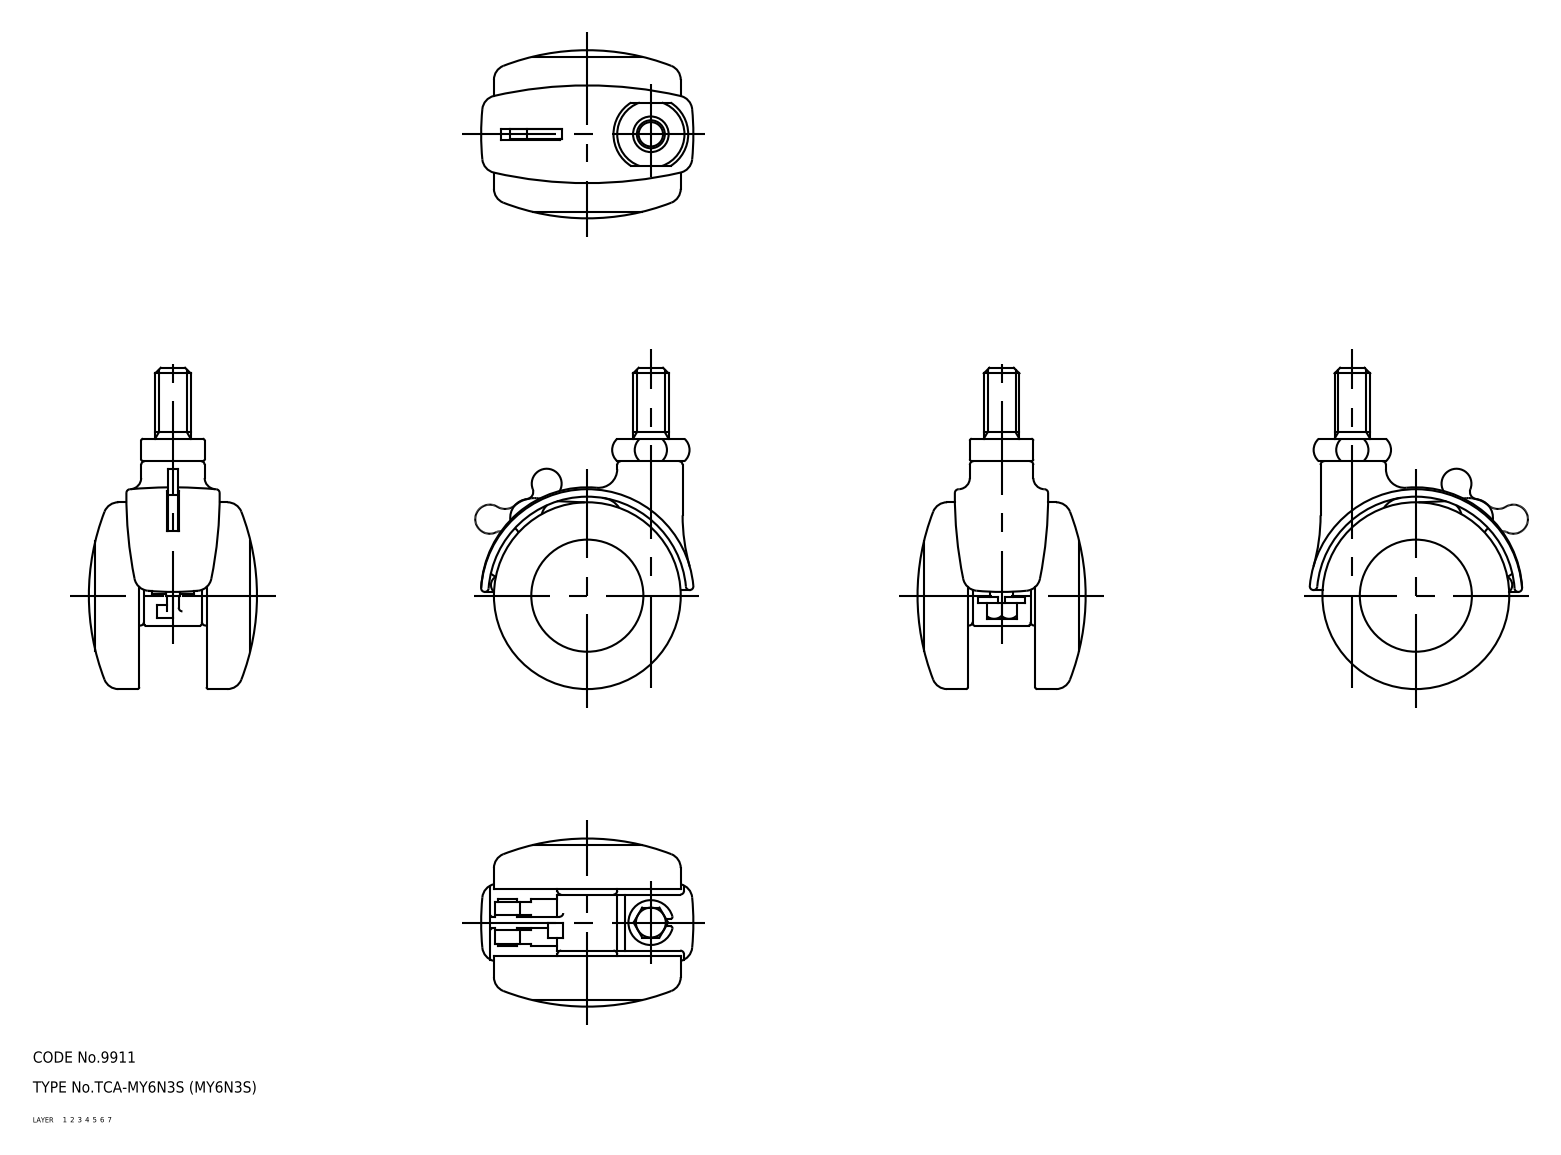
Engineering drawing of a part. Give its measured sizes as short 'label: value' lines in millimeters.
name: wheel; main shaft; lever; MY6N3S_15085_36
written by: CADfix (AUTOMOTIVE_DESIGN)
unit: mm
bodies: 6 solids, 212 faces (0 planar, 0 cylindrical, 212 other)
size: 86 × 58.93 × 44.98
volume: 56 474 mm³; area: 28 201 mm²
